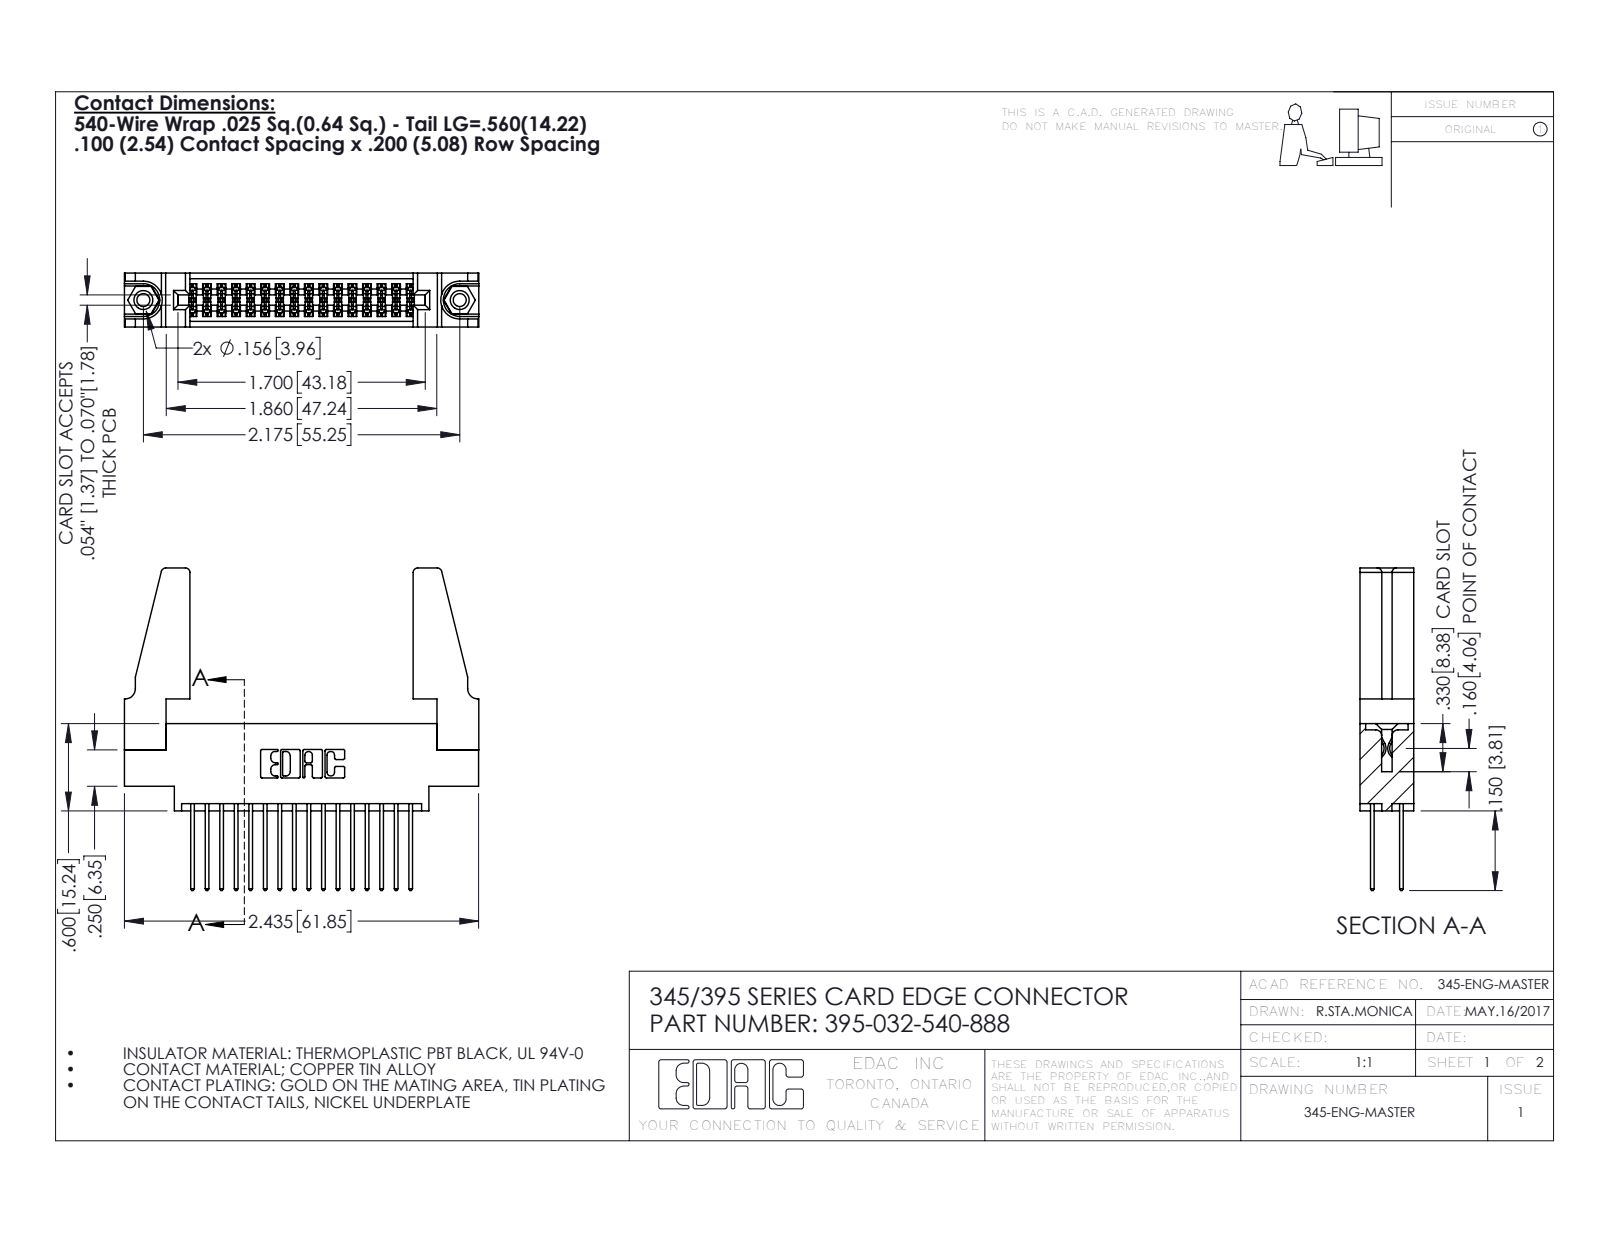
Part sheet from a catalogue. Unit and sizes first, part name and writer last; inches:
Units: inches
Overall size (bounding box): 2.436 × 2.217 × 0.37
Round holes (diameter × count): ⌀0.089 ×2, ⌀0.125 ×2, ⌀0.156 ×2, ⌀0.064 ×1
Round bosses / shafts (diameter × count): ⌀0.155 ×2
Partial cylindrical surfaces — rounded edges, fillets, slot ends (radius × count): R0.006 ×48, R0.01 ×32, R0.01 ×22, R0.03 ×8, R0.007 ×6, R0.031 ×6, R0.026 ×3, R0.014 ×2
Main face-to-face distances: 0.37, 0.072, 0.298, 0.2, 0.098, 0.272, 0.025, 0.225, 0.175, 0.148
Hole centre spacings: 0.27, 1.942, 2.175
Volume: 0.551 in³ · Surface area: 18.39 in²
Bodies: 37 solids, 1854 faces (1212 planar, 626 cylindrical, 16 other)
Part name (STEP PRODUCT): 345 Part_0.170 Offset - 0.156 Dia-TH; 395-032-540-888; 345-220-078_345-220-088; 345-292-001_345-293-140 (+1 more)
STEP written by: SolidWorks 2016 (CONFIG_CONTROL_DESIGN)
